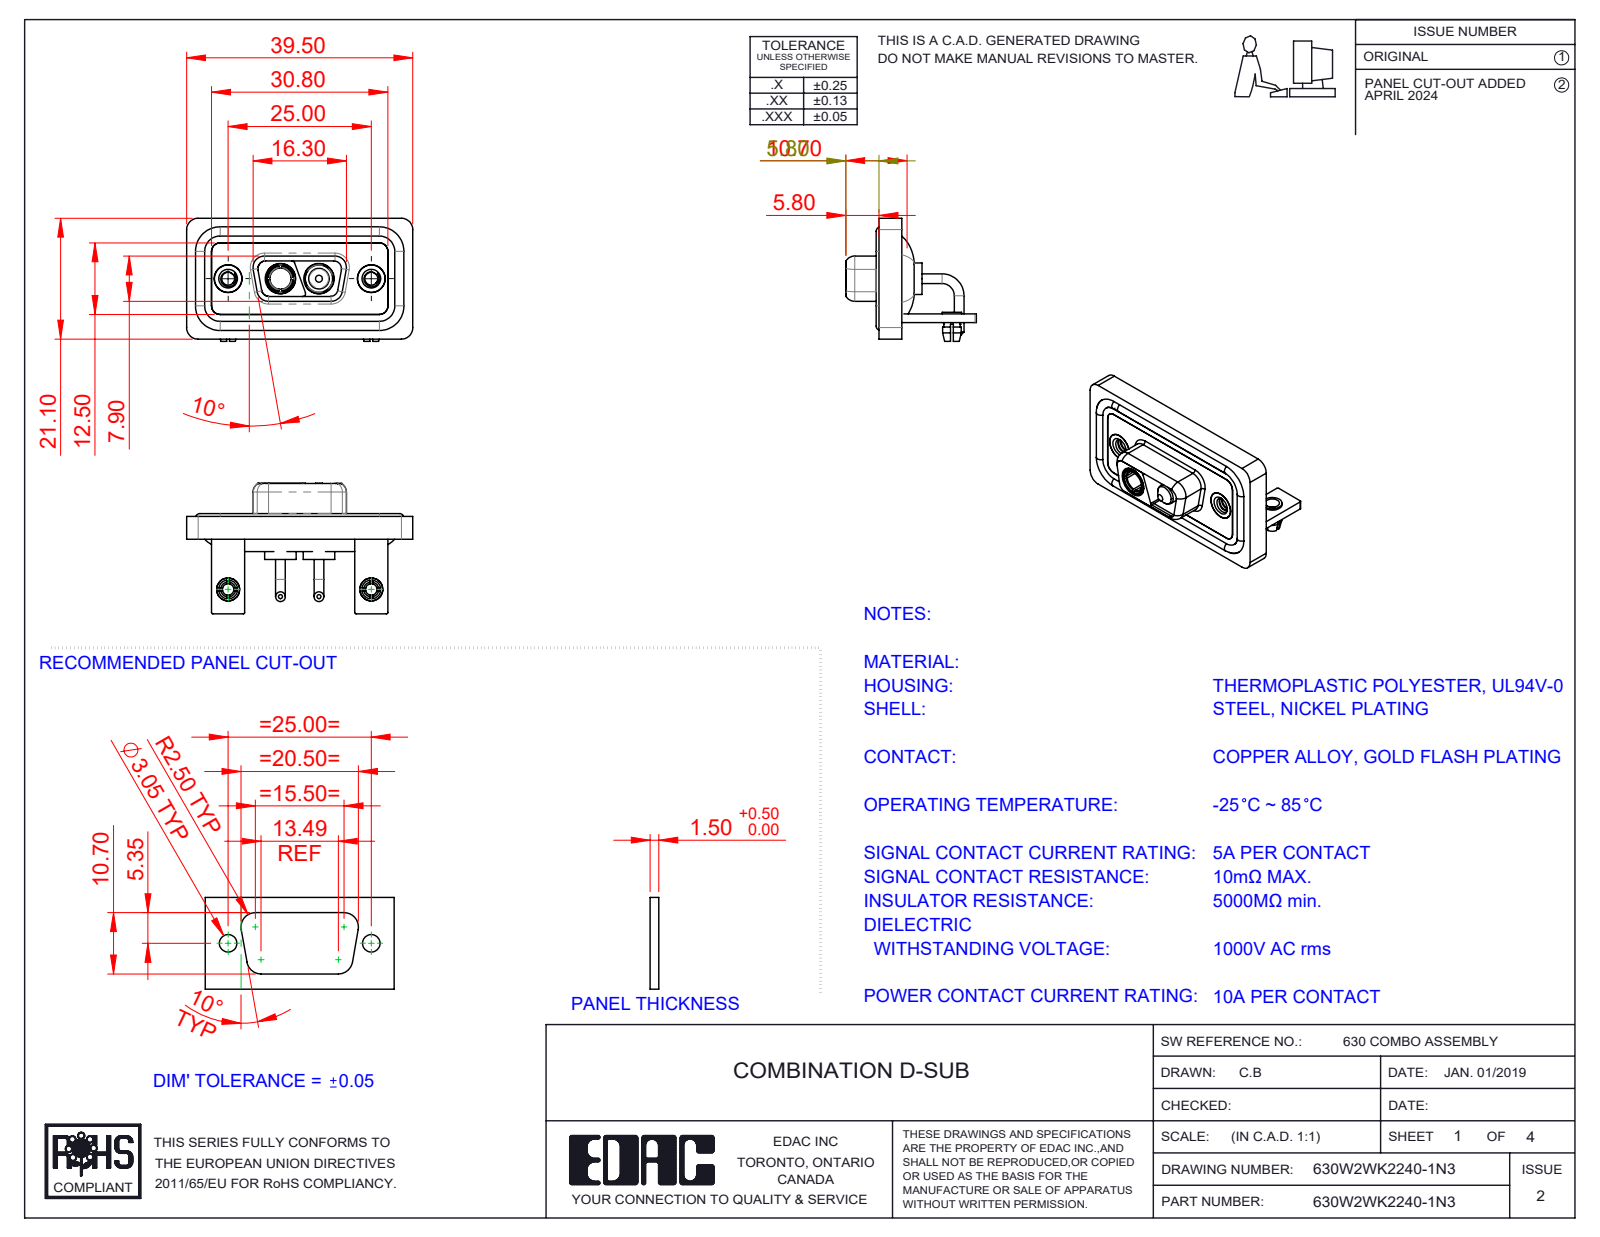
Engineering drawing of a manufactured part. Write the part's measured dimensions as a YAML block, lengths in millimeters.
part_name: "630Combo Shell Rear_09 Contacts; 630Combo Threaded Rivet_2; 630Combo Housing_2WK2; 630Combo Shell Front_09 Contacts (+6 more)"
step_written_by: "SolidWorks 2023 (CONFIG_CONTROL_DESIGN)"
units: millimeters
bodies: {solids: 15, faces: 648, planar: 212, cylindrical: 291, other: 145}
overall_size: [39.5, 22.8, 21.5]
volume: 4994
surface_area: 8338
round_holes:
  - {diameter: 4.85, count: 4}
  - {diameter: 2, count: 2}
  - {diameter: 2.26, count: 2}
  - {diameter: 2.5, count: 2}
  - {diameter: 3.2, count: 2}
  - {diameter: 4, count: 2}
  - {diameter: 4.05, count: 2}
  - {diameter: 5, count: 2}
  - {diameter: 5.3, count: 2}
  - {diameter: 3.7, count: 1}
round_bosses_or_shafts:
  - {diameter: 1.7, count: 4}
  - {diameter: 1.6, count: 4}
  - {diameter: 5.5, count: 2}
  - {diameter: 5.2, count: 2}
  - {diameter: 4.95, count: 2}
  - {diameter: 4.8, count: 2}
  - {diameter: 4.75, count: 2}
  - {diameter: 4, count: 2}
partial_cylinders:
  - {radius: 2, count: 19}
  - {radius: 1.5, count: 18}
  - {radius: 0.25, count: 16}
  - {radius: 1.35, count: 8}
  - {radius: 1.6, count: 8}
  - {radius: 0.5, count: 7}
  - {radius: 0.6, count: 4}
  - {radius: 0.65, count: 4}
face_to_face_distances: [0.4, 2.9, 1.5, 1.1, 3.7, 1.8, 0.8, 2.5, 1.6, 3.1]
hole_center_spacings: [9.14, 15.86, 25, 6.72]
